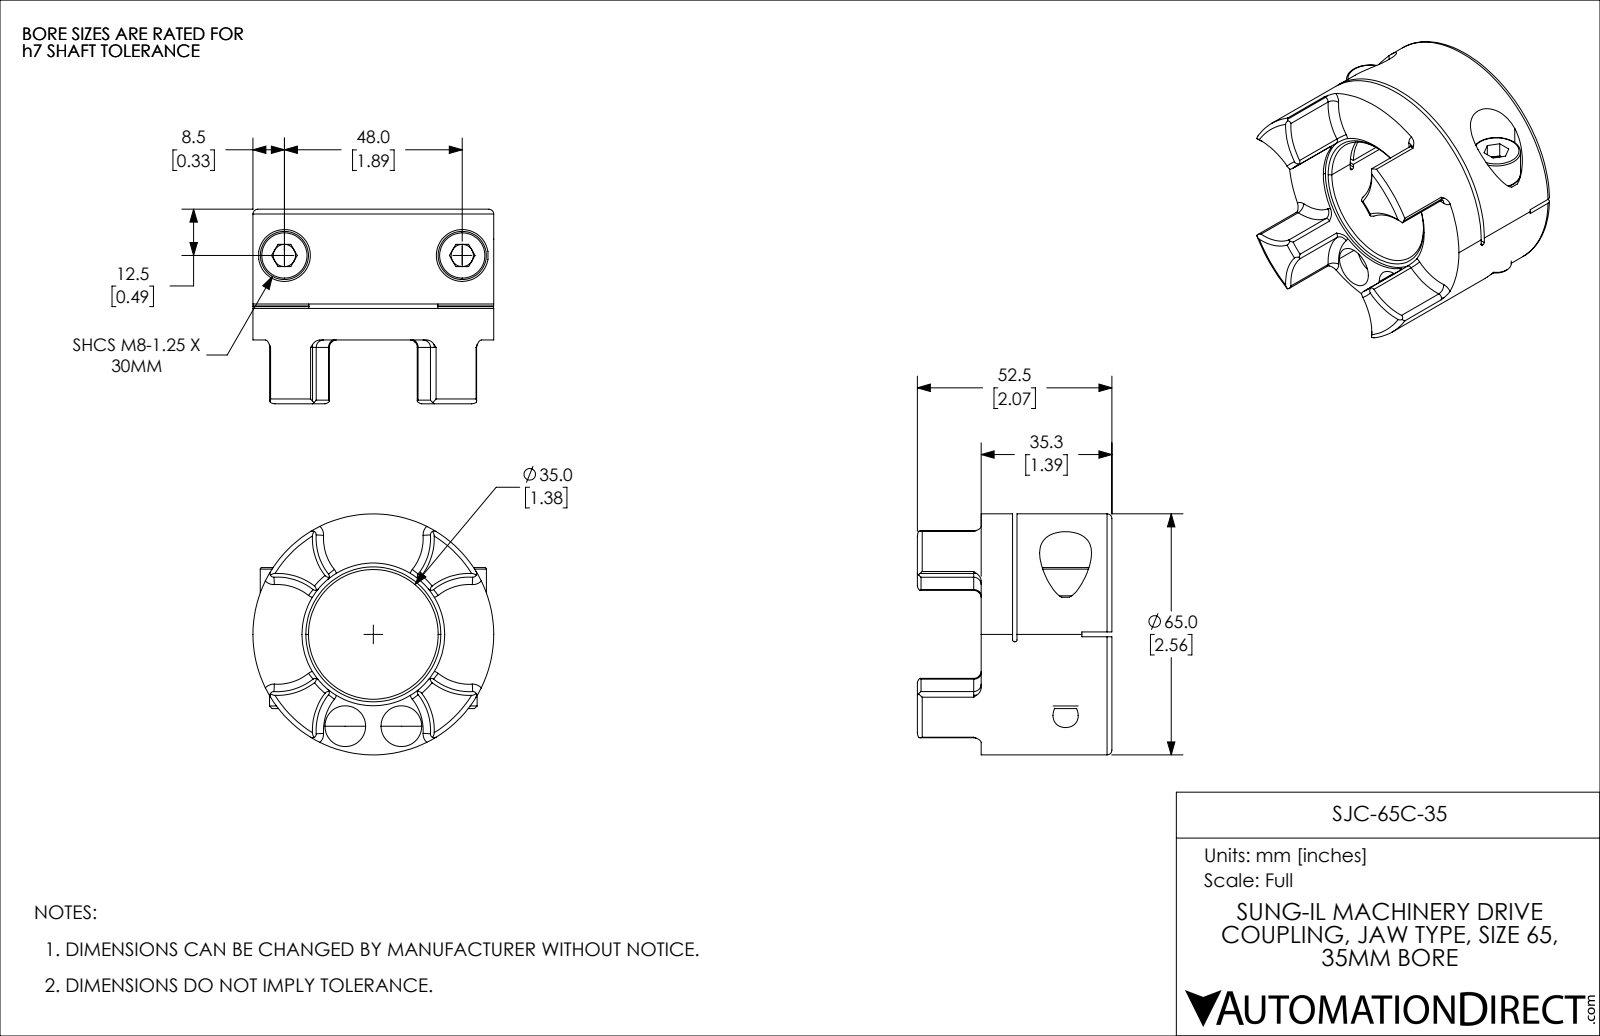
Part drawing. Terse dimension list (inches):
name: SJC-65C-35
written by: SolidWorks 2021 (CONFIG_CONTROL_DESIGN)
unit: in
bodies: 3 solids, 208 faces (52 planar, 74 cylindrical, 82 other)
size: 2.559 × 2.559 × 2.067
volume: 5.316 in³; area: 42.27 in²
holes: 2× ⌀0.236, 2× ⌀0.268, 2× ⌀0.335, 2× ⌀0.433, 2× ⌀0.551, 1× ⌀1.378, 1× ⌀1.516
bosses: 2× ⌀0.512, 2× ⌀0.315, 1× ⌀2.559
rounds: 16× R0.039, 4× R0.608, 2× R0.02, 1× R1.969
face distances: 1.055, 0.047, 1.008, 0.335, 0.382, 1.39, 0.051, 0.677, 1.012, 1.059
hole spacings: 1.019, 0.596, 1.89
